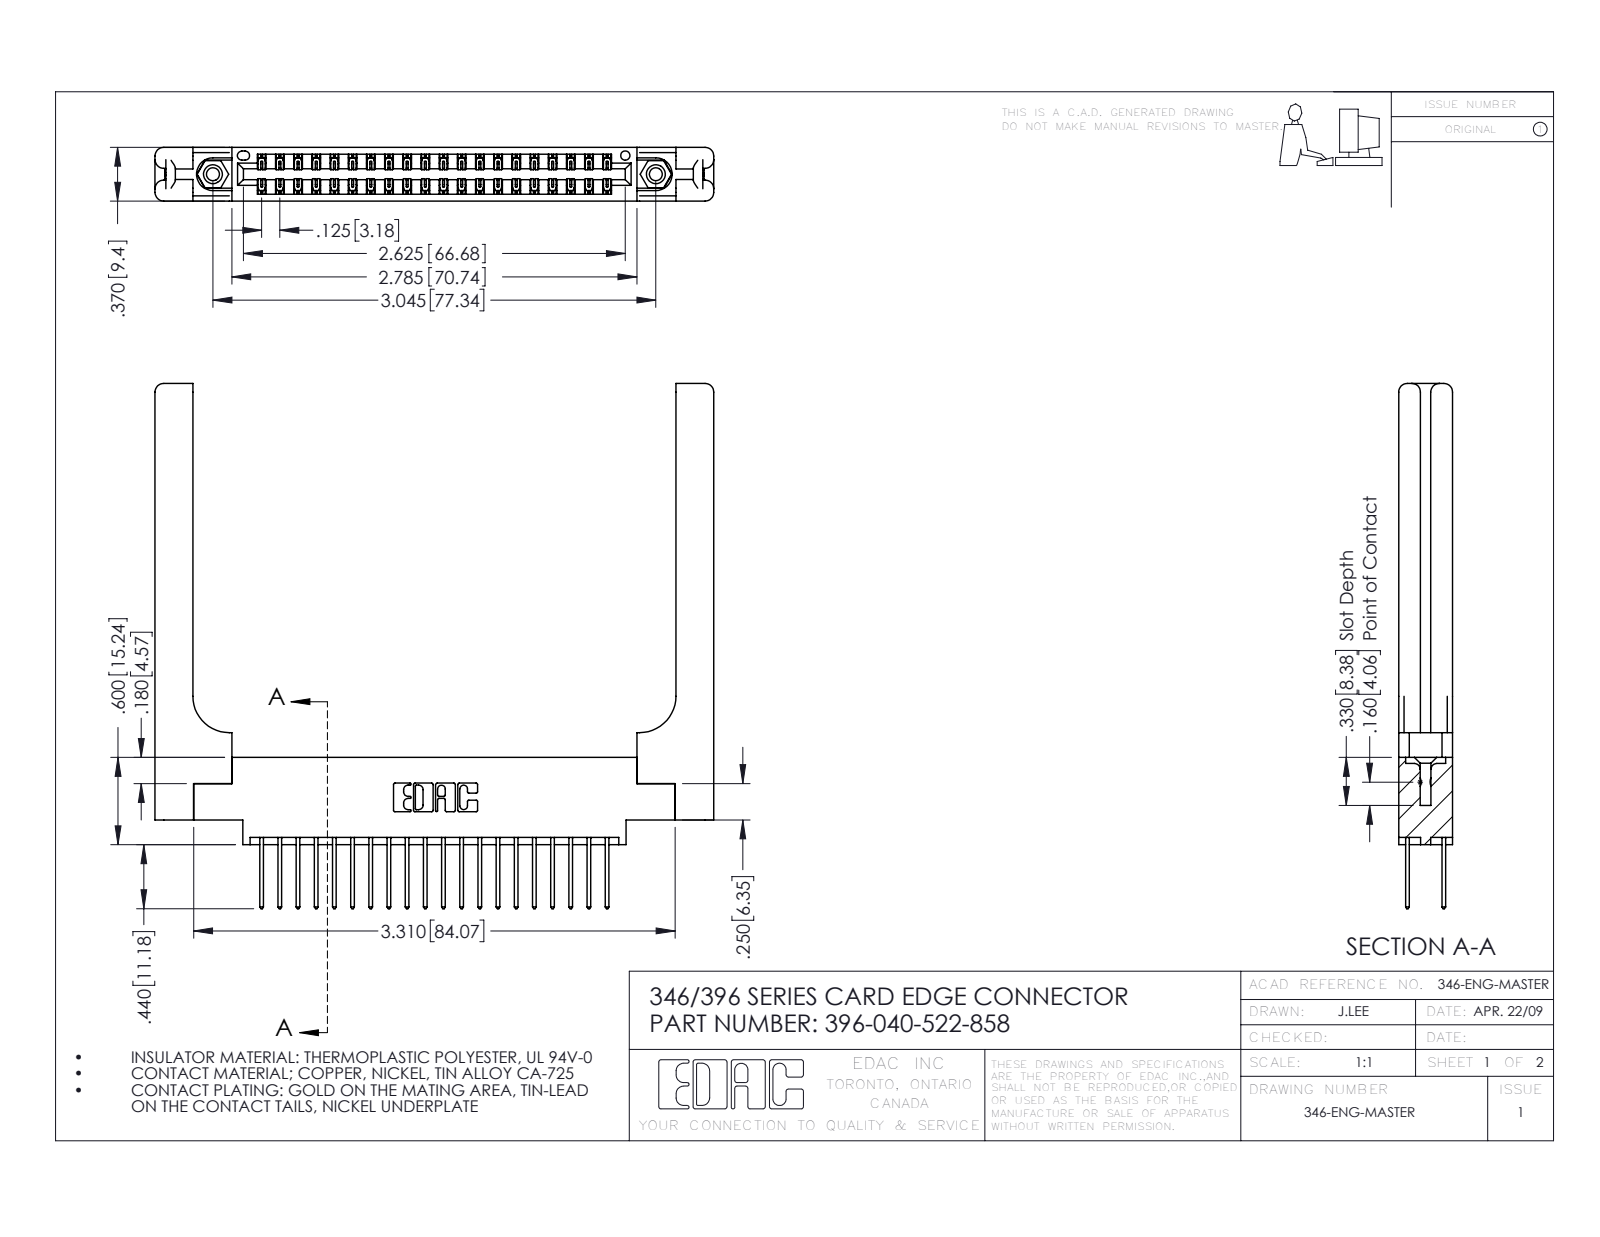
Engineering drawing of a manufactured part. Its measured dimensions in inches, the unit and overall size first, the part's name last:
Units: inches
Overall size (bounding box): 3.841 × 3.61 × 0.37
Round holes (diameter × count): ⌀0.089 ×2, ⌀0.125 ×2, ⌀0.156 ×2, ⌀0.064 ×1
Round bosses / shafts (diameter × count): ⌀0.155 ×2
Partial cylindrical surfaces — rounded edges, fillets, slot ends (radius × count): R0.006 ×60, R0.01 ×40, R0.01 ×22, R0.06 ×16, R0.007 ×6, R0.031 ×6, R0.026 ×3, R0.014 ×2
Main face-to-face distances: 0.37, 0.072, 0.048, 0.322, 0.15, 0.148, 0.25, 0.025, 0.298, 0.275
Hole centre spacings: 0.246, 2.837, 3.045
Volume: 1.024 in³ · Surface area: 27.98 in²
Bodies: 45 solids, 2462 faces (1628 planar, 774 cylindrical, 60 other)
Part name (STEP PRODUCT): 396-040-522-858; 345-250-001_345-250-001-102; 345-292-001_345-293-122; 346 Part_0.170 Offset - 0.156 Dia-TH (+1 more)
STEP written by: SolidWorks 2016 (CONFIG_CONTROL_DESIGN)
